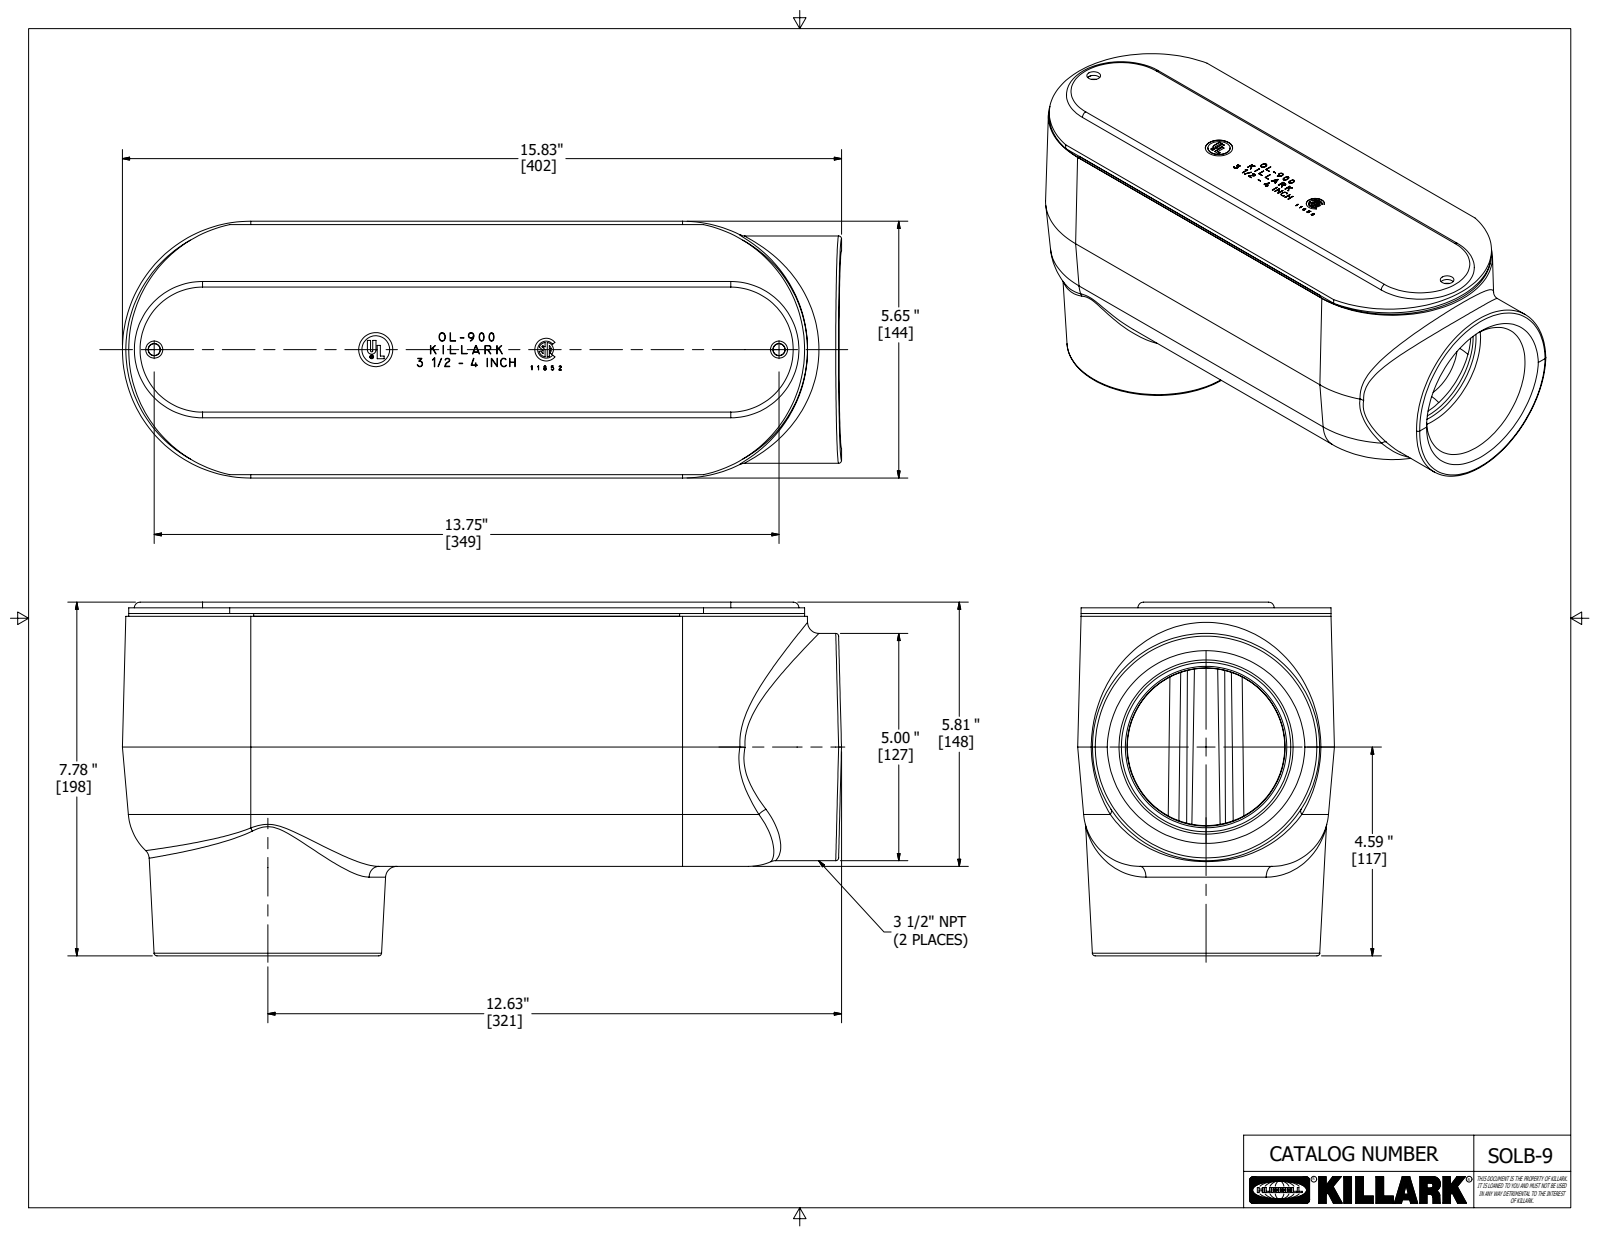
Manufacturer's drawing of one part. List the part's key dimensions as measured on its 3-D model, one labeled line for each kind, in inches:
Part name (STEP PRODUCT): SOLB-9; 17324-1; 03643; 0243900B
STEP written by: Autodesk Inventor 2020 (AUTOMOTIVE_DESIGN)
Units: inches
Bodies: 3 solids, 1617 faces (772 planar, 67 cylindrical, 778 other)
Overall size (bounding box): 15.825 × 7.781 × 5.651
Volume: 98.16 in³ · Surface area: 872.5 in²
Round holes (diameter × count): ⌀0.375 ×3, ⌀0.259 ×2, ⌀0.07 ×1, ⌀0.083 ×1, ⌀0.611 ×1, ⌀0.75 ×1
Round bosses / shafts (diameter × count): ⌀5 ×1, ⌀0.75 ×1, ⌀0.611 ×1, ⌀0.083 ×1, ⌀0.07 ×1
Partial cylindrical surfaces — rounded edges, fillets, slot ends (radius × count): R0.062 ×8, R0.125 ×6, R0.25 ×3, R0.008 ×2, R0.013 ×2, R0.024 ×2, R0.094 ×2, R1.25 ×2
Main face-to-face distances: 0.063, 0.125, 0.188, 0.125, 0.25, 0.313, 5.656, 5.344, 5.406, 5.531
Hole centre spacings: 0.183, 2, 6.875, 1.917, 2.096, 4.787, 4.875, 6.787
